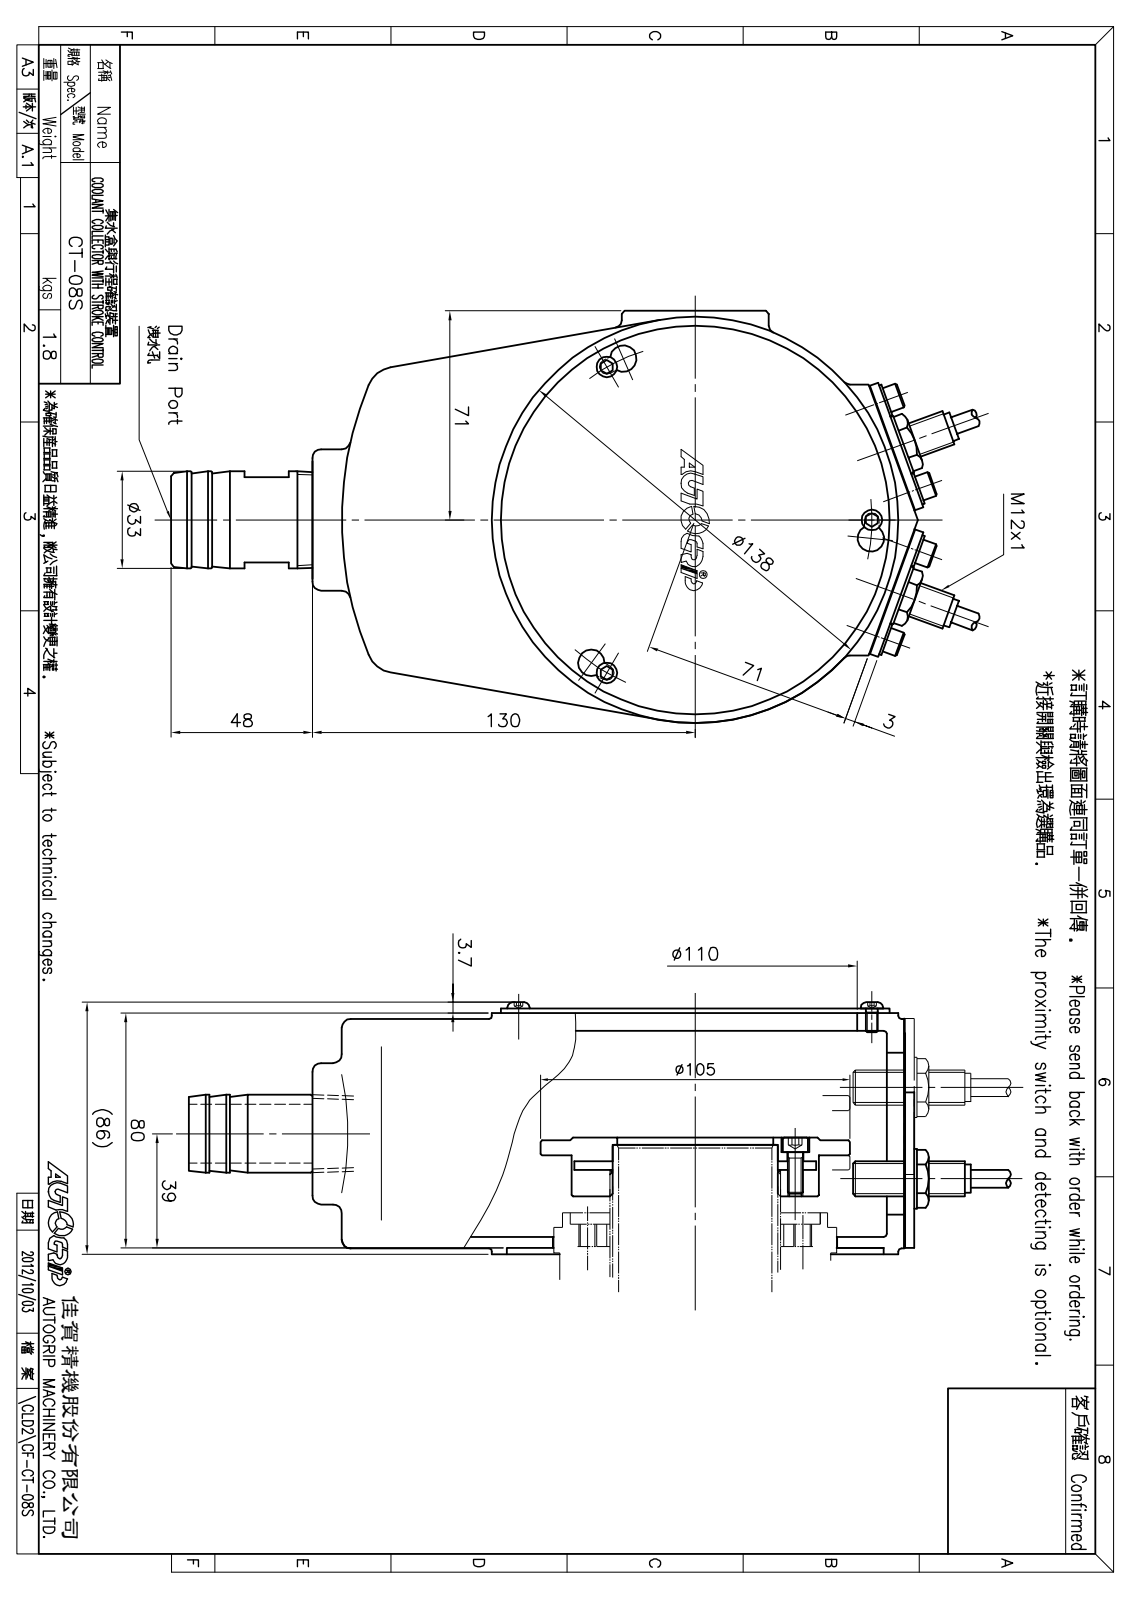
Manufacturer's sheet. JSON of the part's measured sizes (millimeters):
{"part_name": "CT-08集水盒本體; CT-08洩油管; CF-CT-S08-14000; CF-CT-08S (+1 more)", "step_written_by": "SolidWorks 2016 (CONFIG_CONTROL_DESIGN)", "units": "millimeters", "bodies": {"solids": 15, "faces": 457, "planar": 213, "cylindrical": 139, "other": 105}, "overall_size": [258.35, 140, 85.5], "volume_mm3": 478438, "surface_area_mm2": 237280, "round_holes": [[5, 4], [4, 3], [4.1, 2], [5.5, 2], [9.5, 2], [12, 2], [25, 1], [53, 1], [56, 1], [56.5, 1], [82, 1], [96.5, 1]], "round_bosses_or_shafts": [[8.5, 4], [7, 3], [5, 2], [138, 1], [132, 1], [105, 1], [84, 1], [45, 1]], "partial_cylinders_radius": [[2.75, 16], [3, 10], [7, 8], [2, 6], [2.5, 2], [6, 2], [10, 2], [65, 1]], "face_to_face_distances": [4, 6, 1.5, 7.5, 76, 74, 2, 77.5, 70, 0.5], "hole_center_spacings": [60, 103.92, 20.59, 20.6, 32, 34, 52.11, 82.44]}
